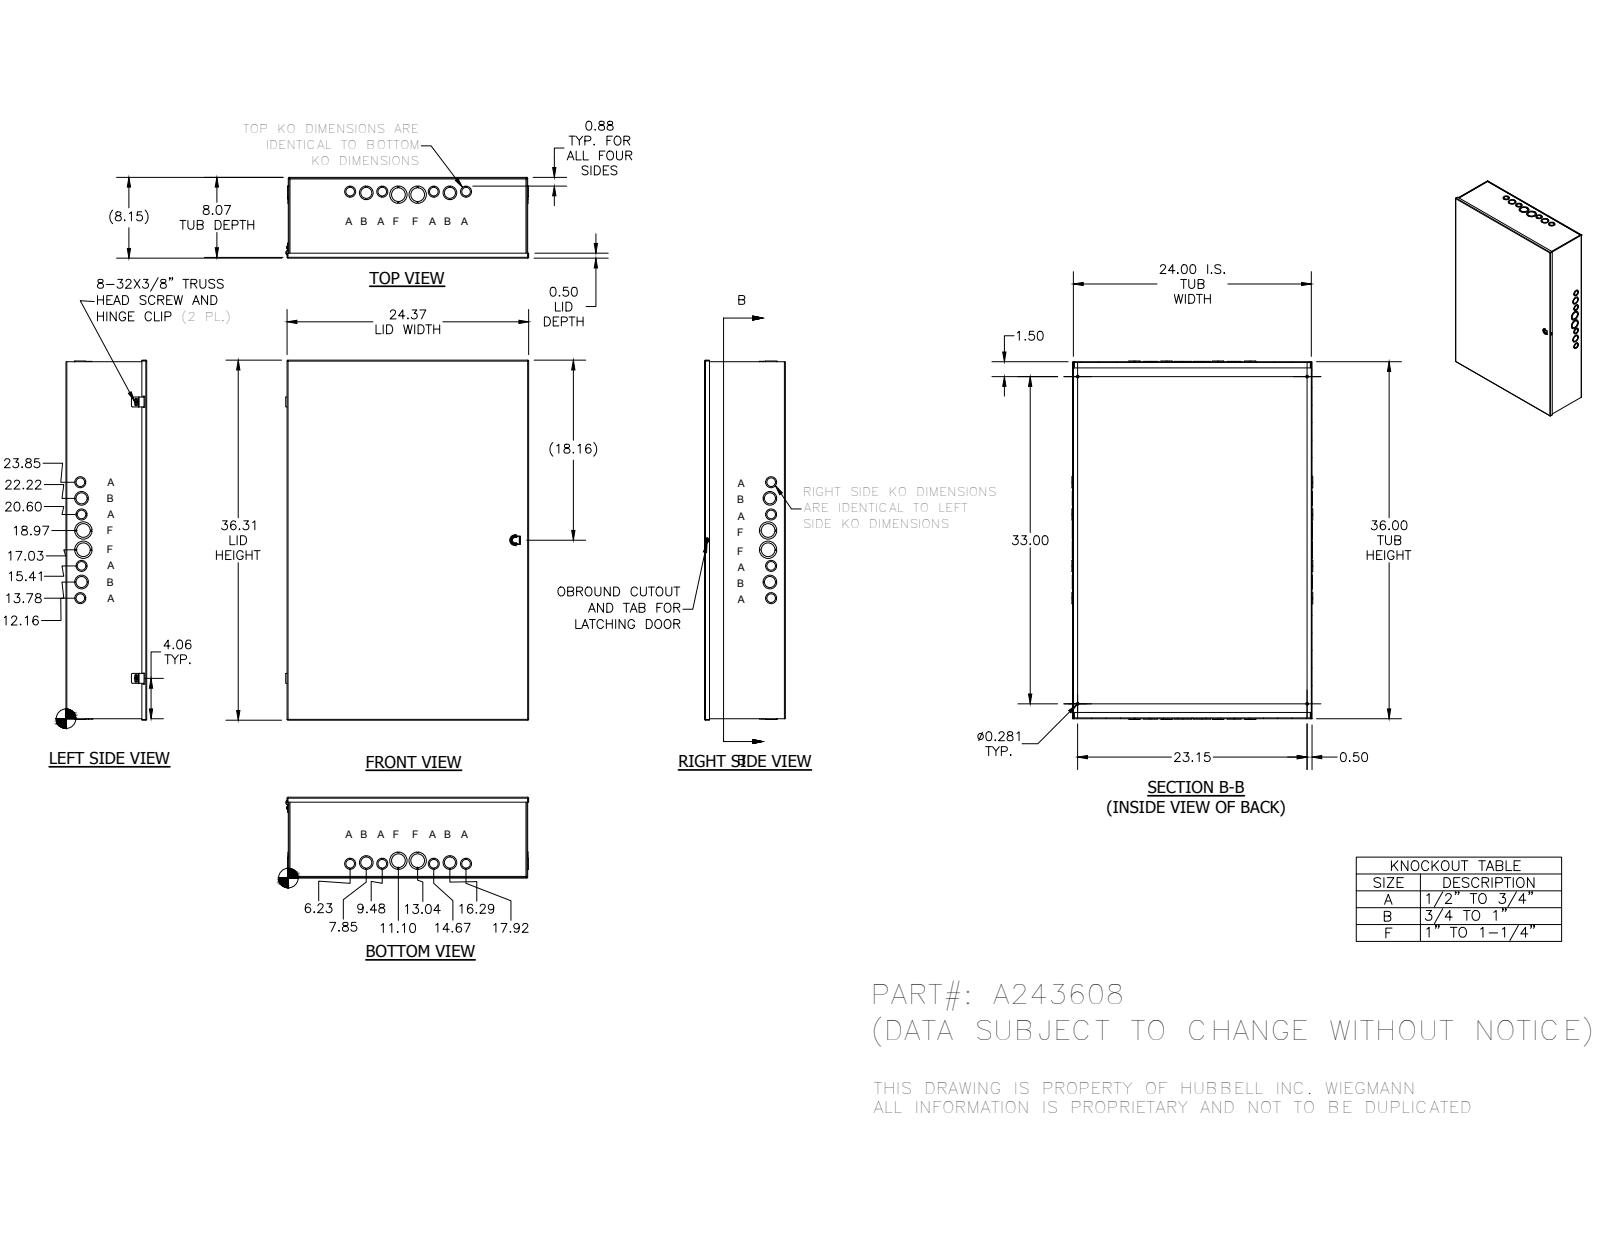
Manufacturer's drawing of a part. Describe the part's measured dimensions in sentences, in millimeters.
The part is named "A243608BLR; A2408TB; A2436LFA; 31816 (+3 more)". Its 3-D file was written by "Autodesk Inventor 2014 (AUTOMOTIVE_DESIGN)". It is 38 solids with 1287 faces: 941 planar, 281 cylindrical and 65 other. Overall it measures 922.31 by 623.39 by 207.01 millimeters. Round holes: 14 of diameter 28.57, 10 of diameter 22.22, 8 of diameter 34.92, 4 of diameter 7.14, 4 of diameter 44.45, 2 of diameter 3.56. Round bosses or shafts: 2 of diameter 9.75, 2 of diameter 4.17. Partial cylindrical surfaces (rounded edges, fillets, slot ends): 12 of radius 0.4, 12 of radius 2.28, 10 of radius 0.79, 8 of radius 1.59, 7 of radius 3.17, 4 of radius 0.79, 4 of radius 1.78, 4 of radius 2.37. The main face-to-face distances are 1.88, 1.57, 205.13, 203.56, 205.44, 207.01, 611.48, 912.52, 609.6, 613.36. The hole center spacings are 41.39, 41.4, 42.03, 82.55, 82.69, 90.9, 124.07, 131.92.
